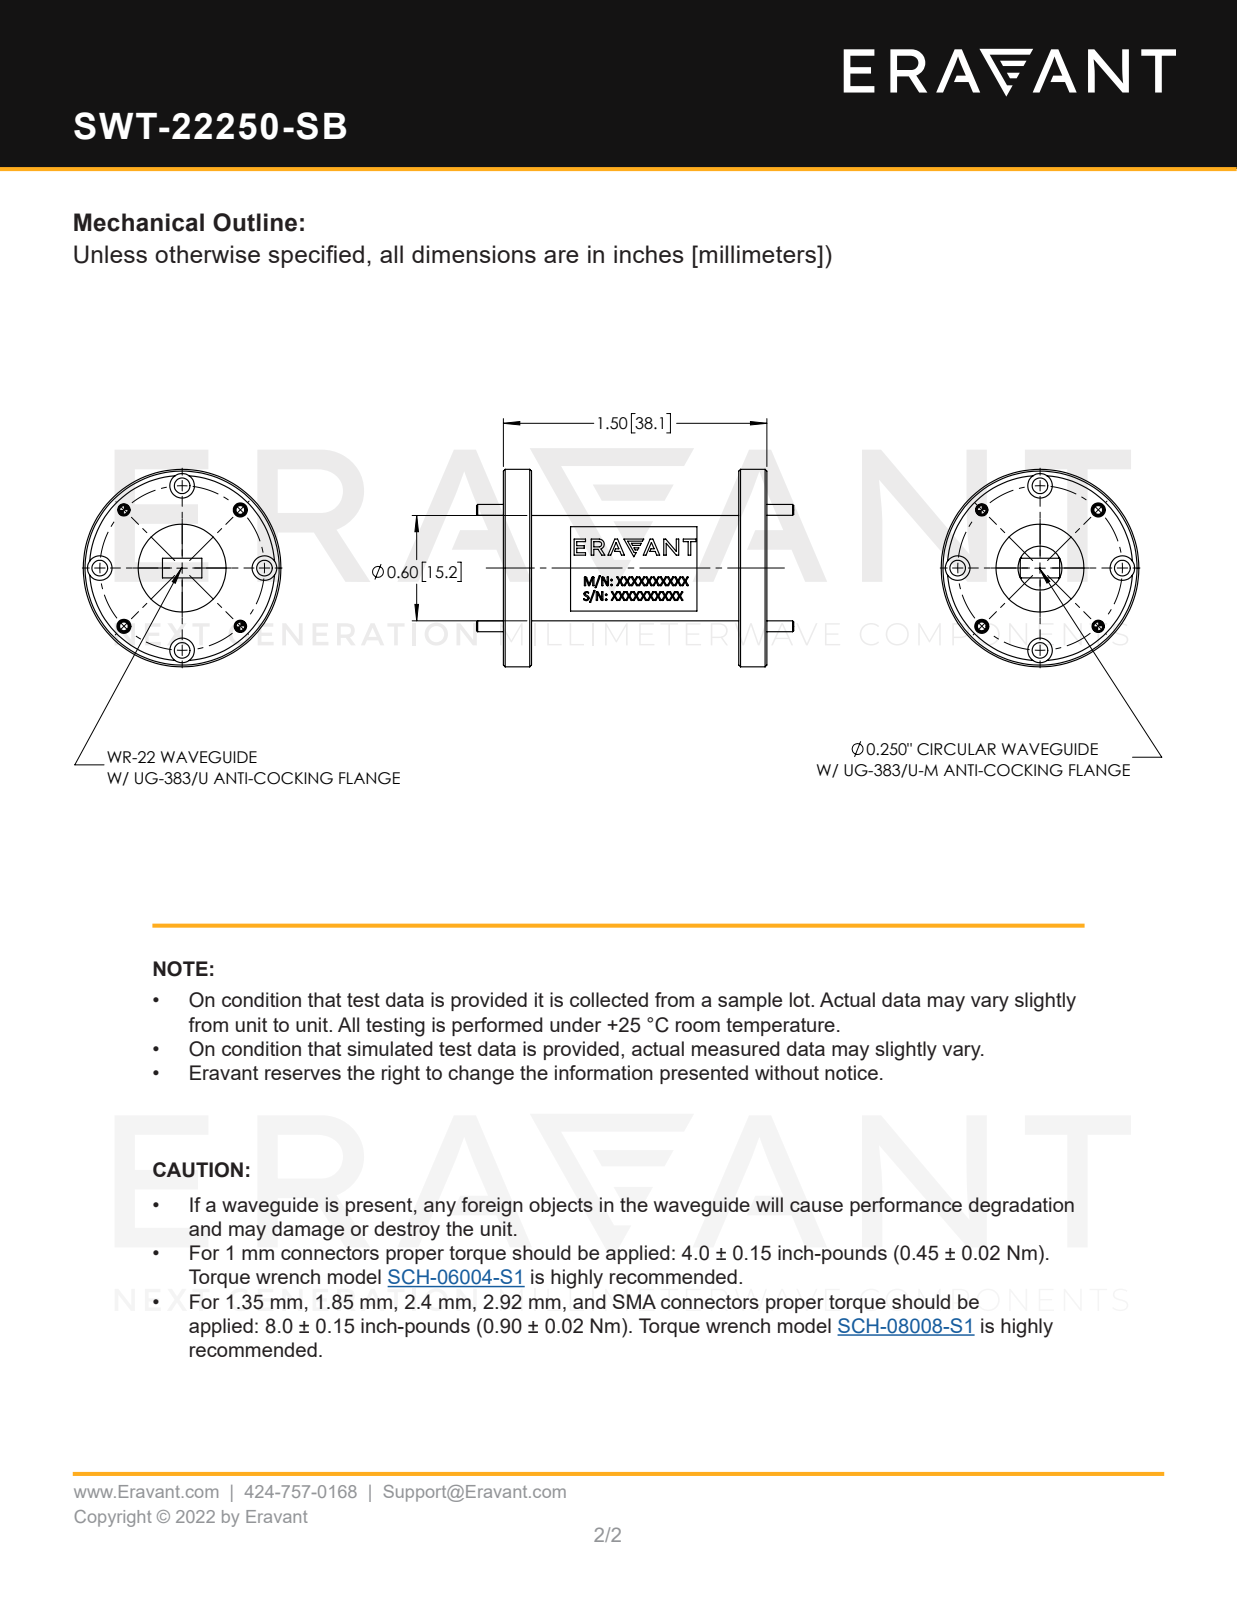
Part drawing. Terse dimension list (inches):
name: WT-QC-250-A
written by: SolidWorks 2021 (AUTOMOTIVE_DESIGN)
unit: in
bodies: 5 solids, 148 faces (26 planar, 74 cylindrical, 48 other)
size: 1.805 × 1.125 × 1.125
volume: 0.613 in³; area: 7.591 in²
holes: 4× ⌀0.061, 4× ⌀0.067, 4× ⌀0.089, 4× ⌀0.14, 1× ⌀1.055
bosses: 4× ⌀0.063, 1× ⌀1.125, 1× ⌀0.6, 1× ⌀0.5
face distances: 0.14, 1.32, 1.18, 1.46, 0.02, 0.16, 1.34, 1.48, 1.5, 1.49
hole spacings: 0.359, 0.469, 0.663, 0.866, 0.938
